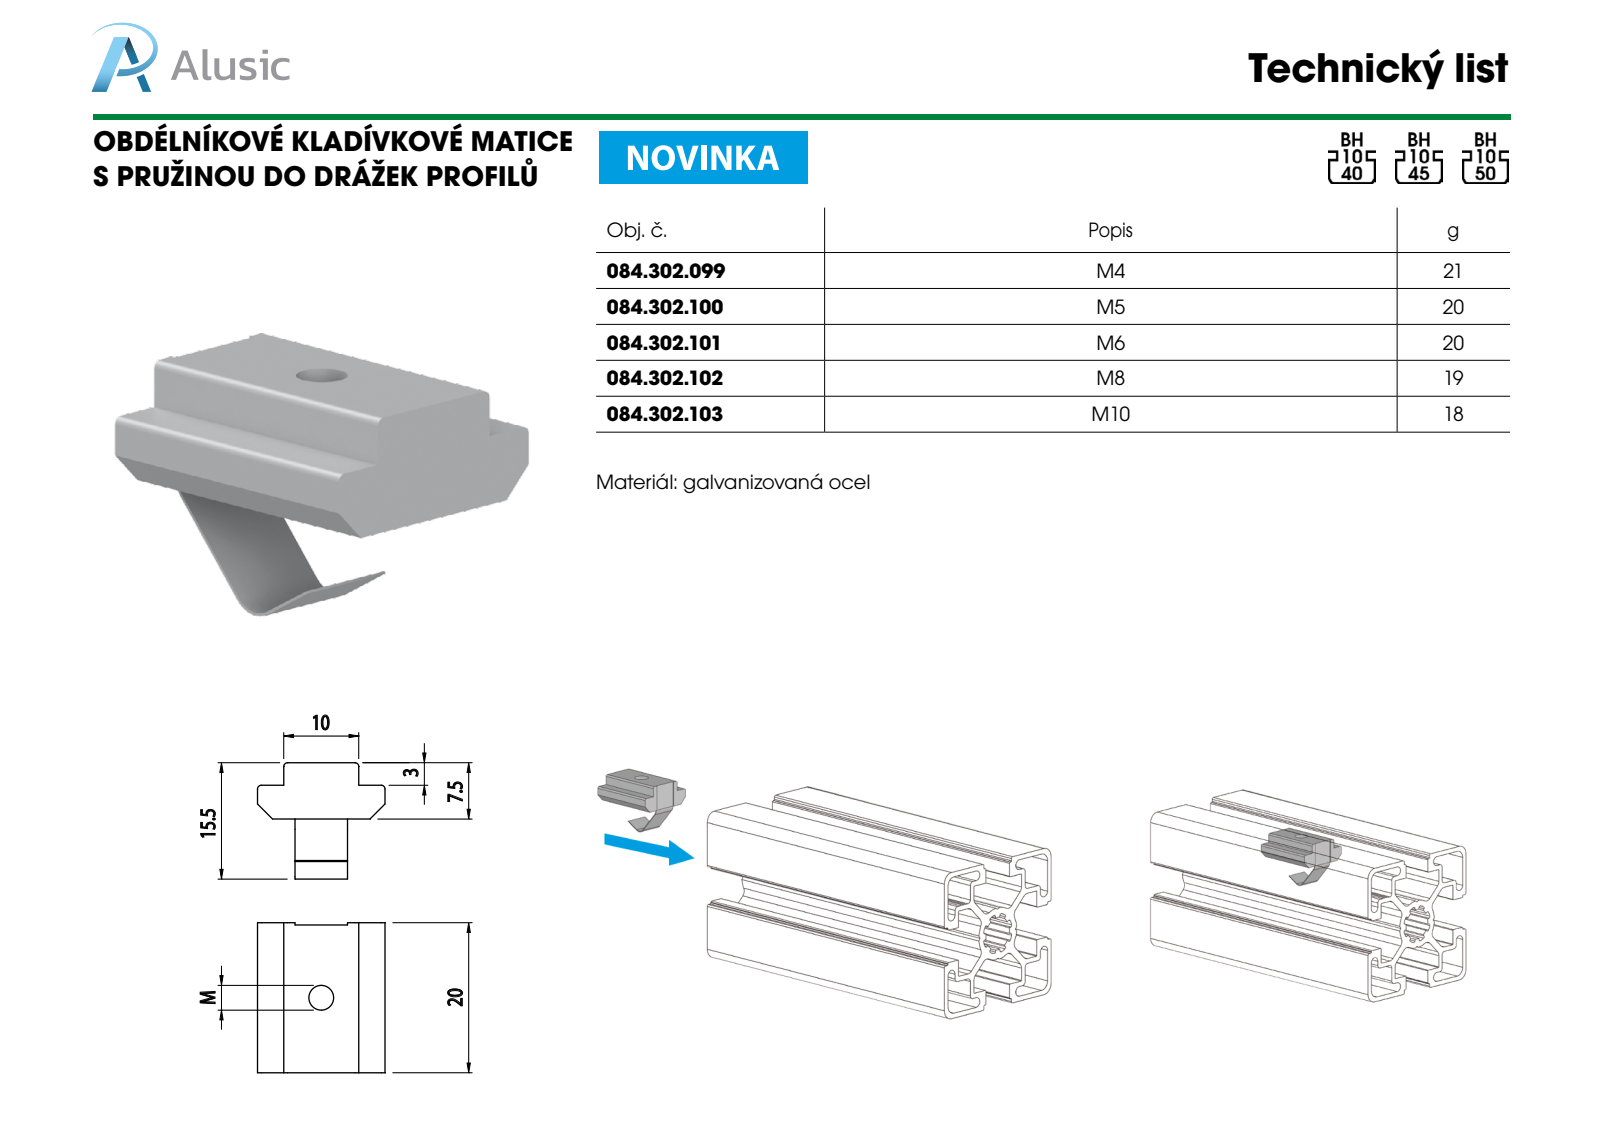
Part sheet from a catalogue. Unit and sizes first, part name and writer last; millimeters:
Units: millimetres
Overall size (bounding box): 20 × 15.5 × 15
Round holes (diameter × count): ⌀6.8 ×1
Partial cylindrical surfaces — rounded edges, fillets, slot ends (radius × count): R0.5 ×4, R2 ×2, R2.2 ×2
Main face-to-face distances: 7.5, 4.5, 3, 2.5, 12.5, 10, 20, 19.7, 15, 4.75
Volume: 1 552 mm³ · Surface area: 1 266 mm²
Bodies: 1 solid, 34 faces (24 planar, 10 cylindrical, 0 other)
Part name (STEP PRODUCT): 084.302.102
STEP written by: SolidWorks 2016 (CONFIG_CONTROL_DESIGN)
